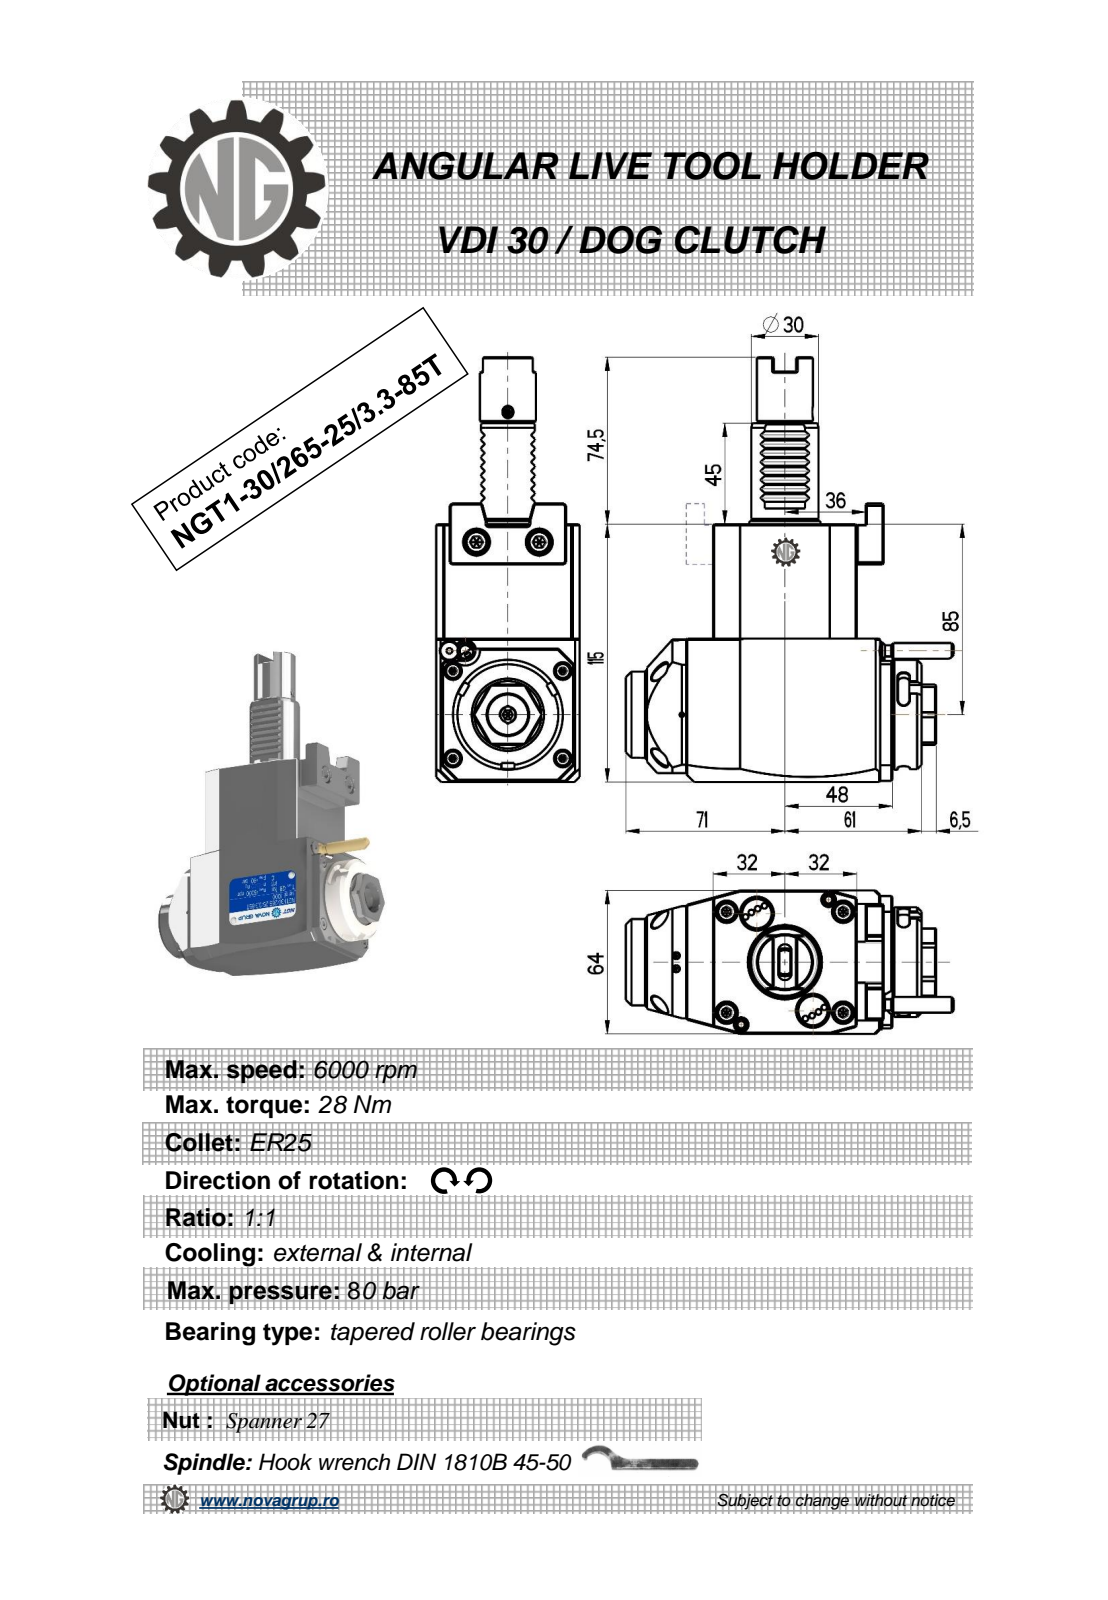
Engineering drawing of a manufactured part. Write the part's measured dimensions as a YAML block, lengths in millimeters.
part_name: "NGT1_30_265_25_3_3_85T"
step_written_by: "PRO/ENGINEER BY PARAMETRIC TECHNOLOGY CORPORATION, 2010280 (CONFIG_CONTROL_DESIGN)"
units: millimeters
bodies: {solids: 1, faces: 368, planar: 231, cylindrical: 73, other: 64}
overall_size: [189.5, 146.38, 64]
volume: 697096
surface_area: 60184
round_holes:
  - {diameter: 2.5, count: 1}
  - {diameter: 3, count: 1}
  - {diameter: 4.2, count: 1}
  - {diameter: 18, count: 1}
round_bosses_or_shafts:
  - {diameter: 49, count: 1}
  - {diameter: 42, count: 1}
  - {diameter: 38.5, count: 1}
  - {diameter: 30, count: 1}
  - {diameter: 25, count: 1}
  - {diameter: 20.85, count: 1}
  - {diameter: 8, count: 1}
  - {diameter: 7, count: 1}
partial_cylinders:
  - {radius: 0.3, count: 16}
  - {radius: 0.26, count: 6}
  - {radius: 2.5, count: 6}
  - {radius: 0.5, count: 2}
  - {radius: 1, count: 2}
  - {radius: 180, count: 2}
  - {radius: 4.5, count: 1}
  - {radius: 15, count: 1}
face_to_face_distances: [64, 115, 80, 16, 4, 12, 93, 51, 76, 17]
hole_center_spacings: [34.25, 108.18, 135]
